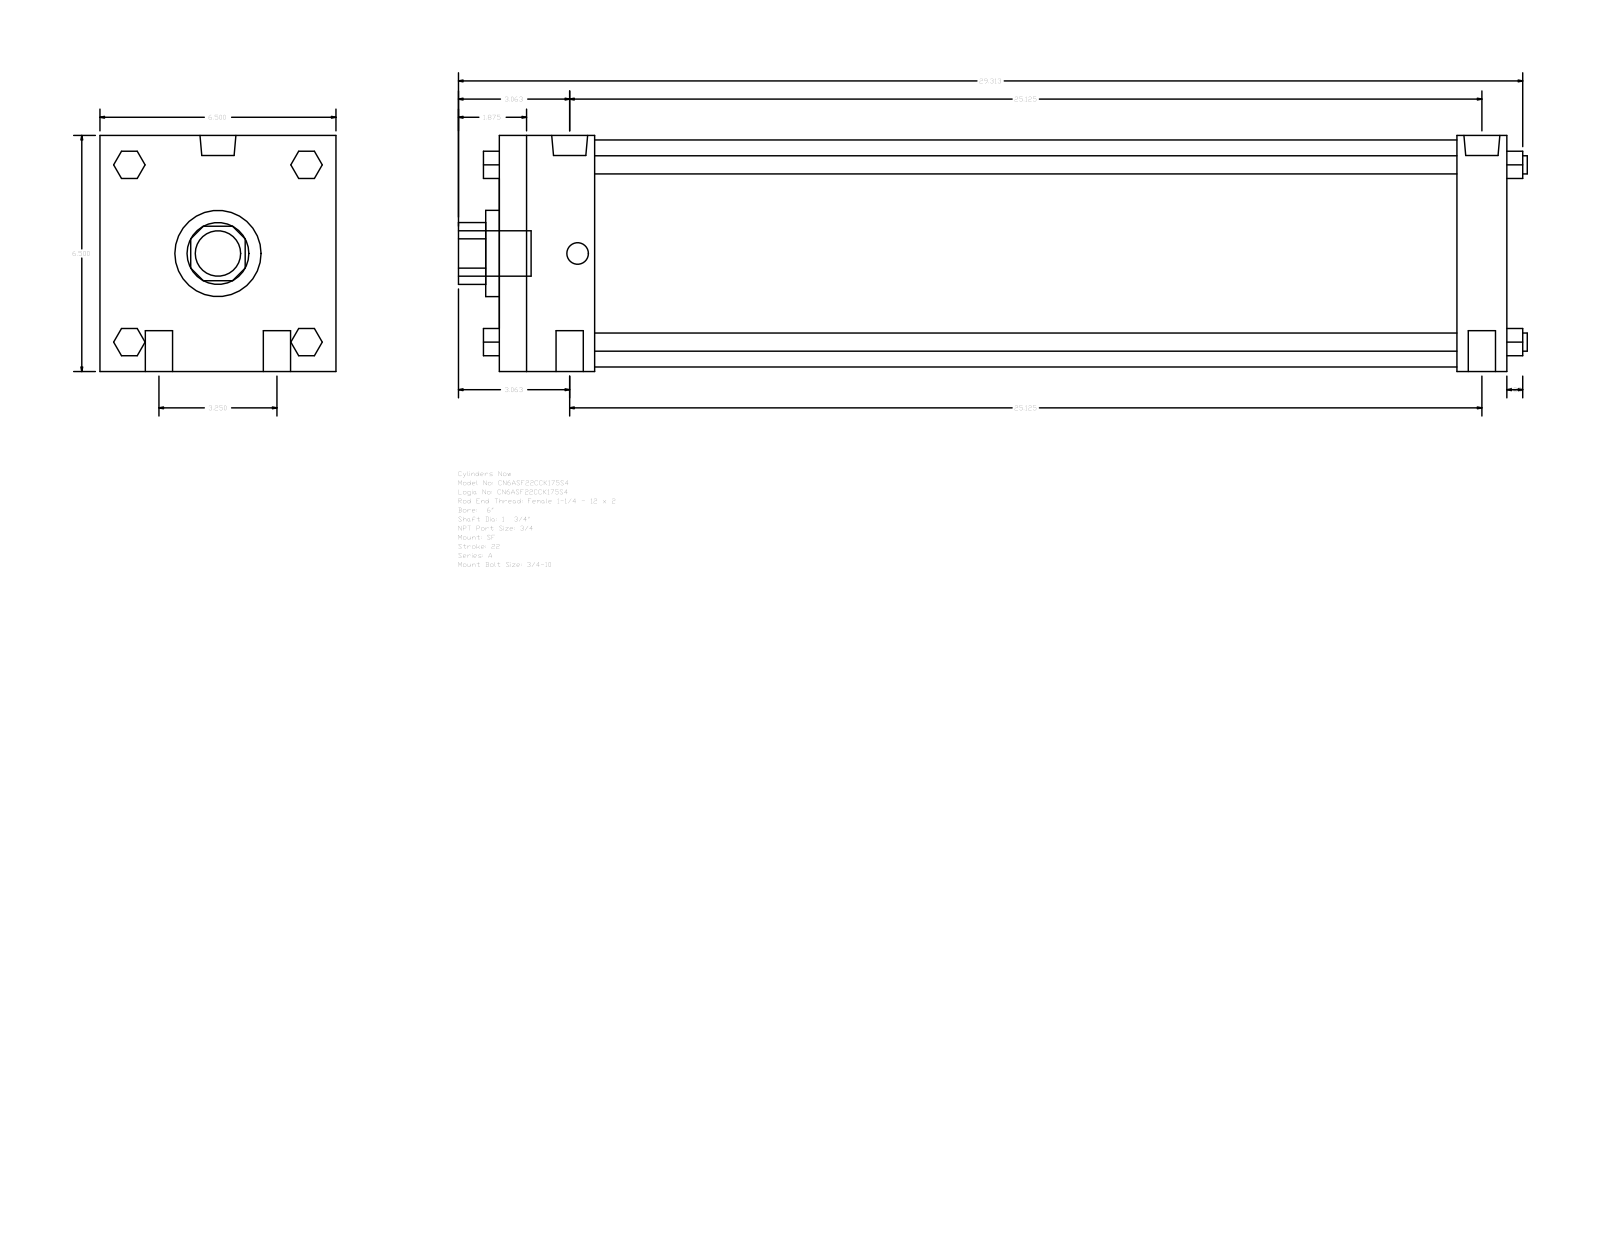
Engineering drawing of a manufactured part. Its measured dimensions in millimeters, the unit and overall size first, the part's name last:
Units: millimetres
Overall size (bounding box): 747.71 × 165.1 × 165.1
Round holes (diameter × count): ⌀44.45 ×1, ⌀60.33 ×1, ⌀158.75 ×1
Round bosses / shafts (diameter × count): ⌀19.05 ×4, ⌀12.7 ×4, ⌀25.12 ×2, ⌀15.08 ×2, ⌀31.75 ×1
Partial cylindrical surfaces — rounded edges, fillets, slot ends (radius × count): R21.63 ×1
Main face-to-face distances: 165.1, 704.85, 34.92, 669.93, 66.68, 603.25, 638.17, 19.05, 61.97, 107.34
Bodies: 0 solids, 124 faces (94 planar, 30 cylindrical, 0 other)
Part name (STEP PRODUCT): A_SF__0600_1.75
STEP written by: GSSL Pune (CONFIG_CONTROL_DESIGN)
